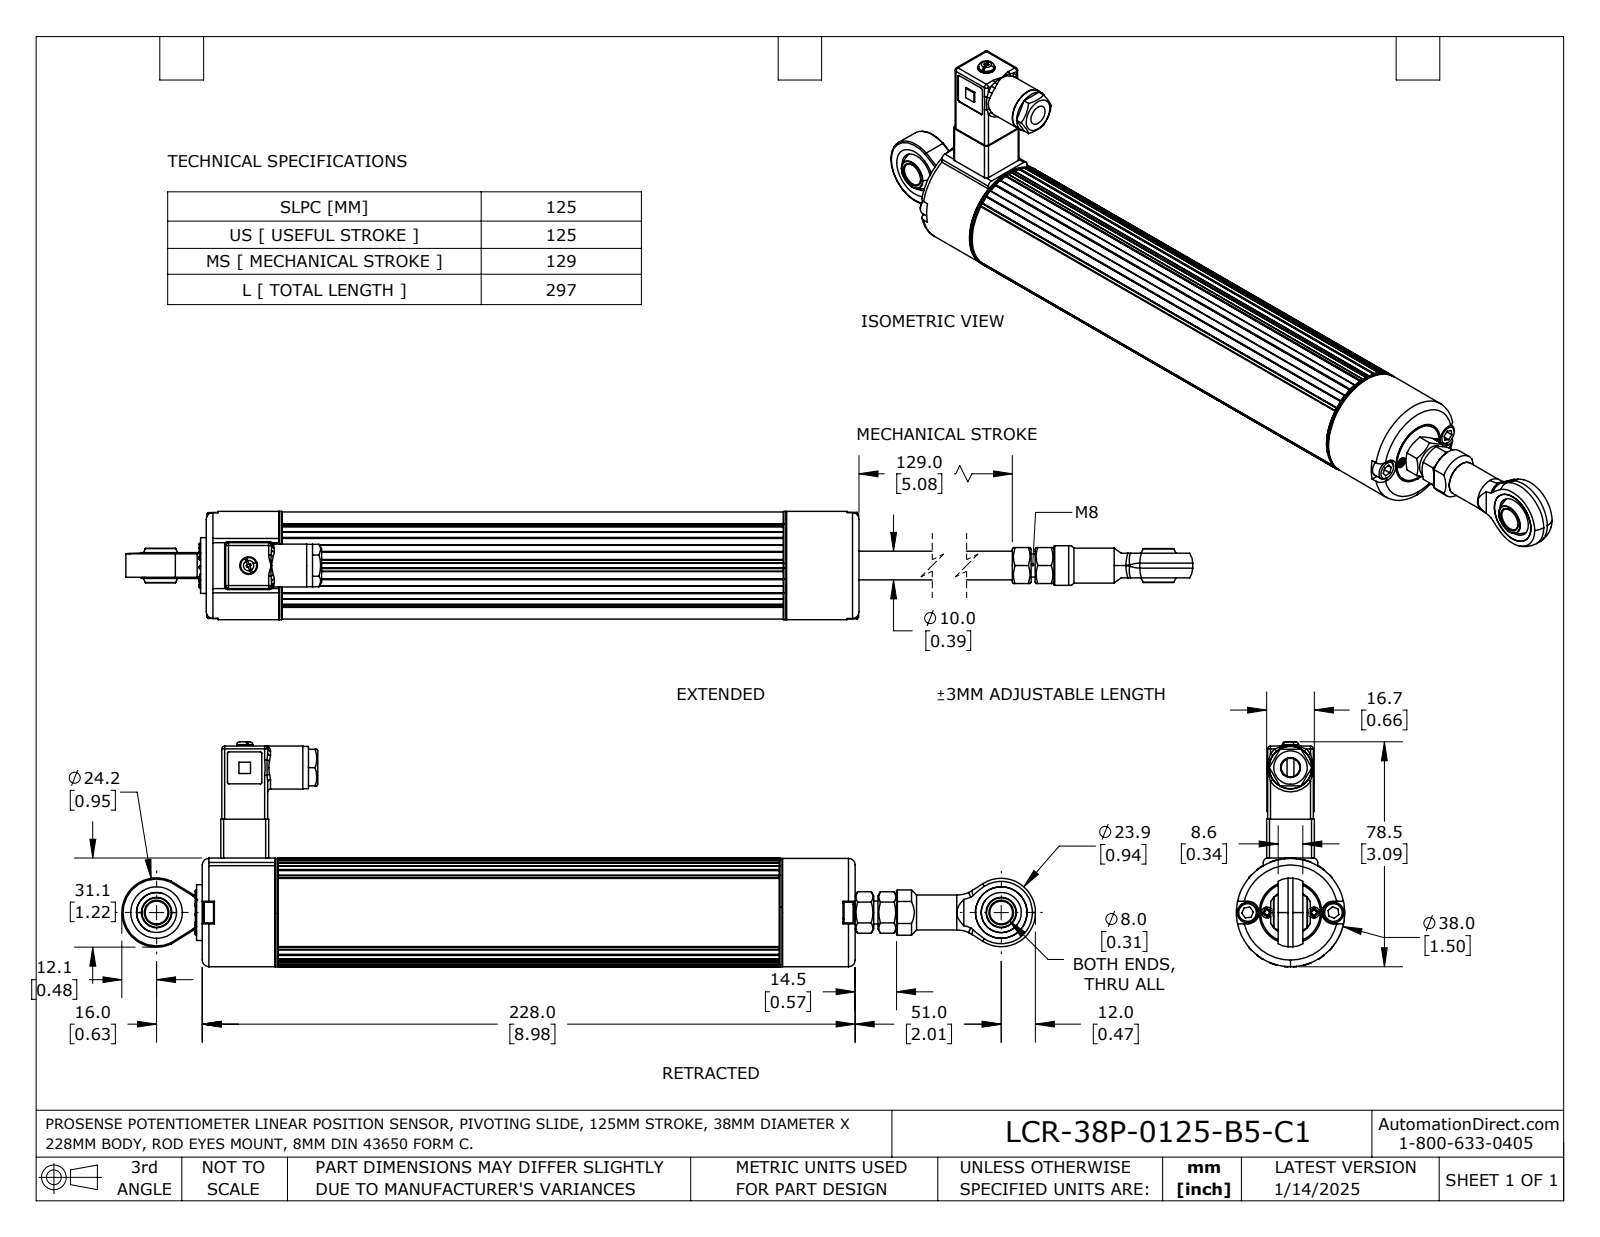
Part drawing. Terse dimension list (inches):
name: LCR-38P-0125-B5-C1
written by: SolidWorks 2023 (AUTOMOTIVE_DESIGN)
unit: in
bodies: 11 solids, 657 faces (295 planar, 210 cylindrical, 152 other)
size: 12.561 × 3.093 × 1.488
volume: 16.66 in³; area: 91.41 in²
holes: 6× ⌀0.102, 4× ⌀0.091, 3× ⌀0.315, 3× ⌀0.551, 2× ⌀0.094, 2× ⌀0.1, 2× ⌀0.111, 2× ⌀0.134, 2× ⌀0.152, 2× ⌀0.165, 1× ⌀0.079, 1× ⌀0.118
bosses: 6× ⌀0.063, 4× ⌀0.283, 4× ⌀0.15, 2× ⌀0.48, 2× ⌀0.079, 1× ⌀1.488, 1× ⌀0.823, 1× ⌀0.768
rounds: 32× R0.008, 20× R0.039, 12× R0.02, 6× R0.016, 2× R0.012, 2× R0.059, 2× R0.083, 2× R0.098
face distances: 6.89, 1.043, 7.933, 0.031, 0.045, 0.612, 0.598, 0.014, 0.644, 0.138
hole spacings: 0.632, 0.075, 0.634, 0.264, 0.268, 0.285, 0.323, 0.394
